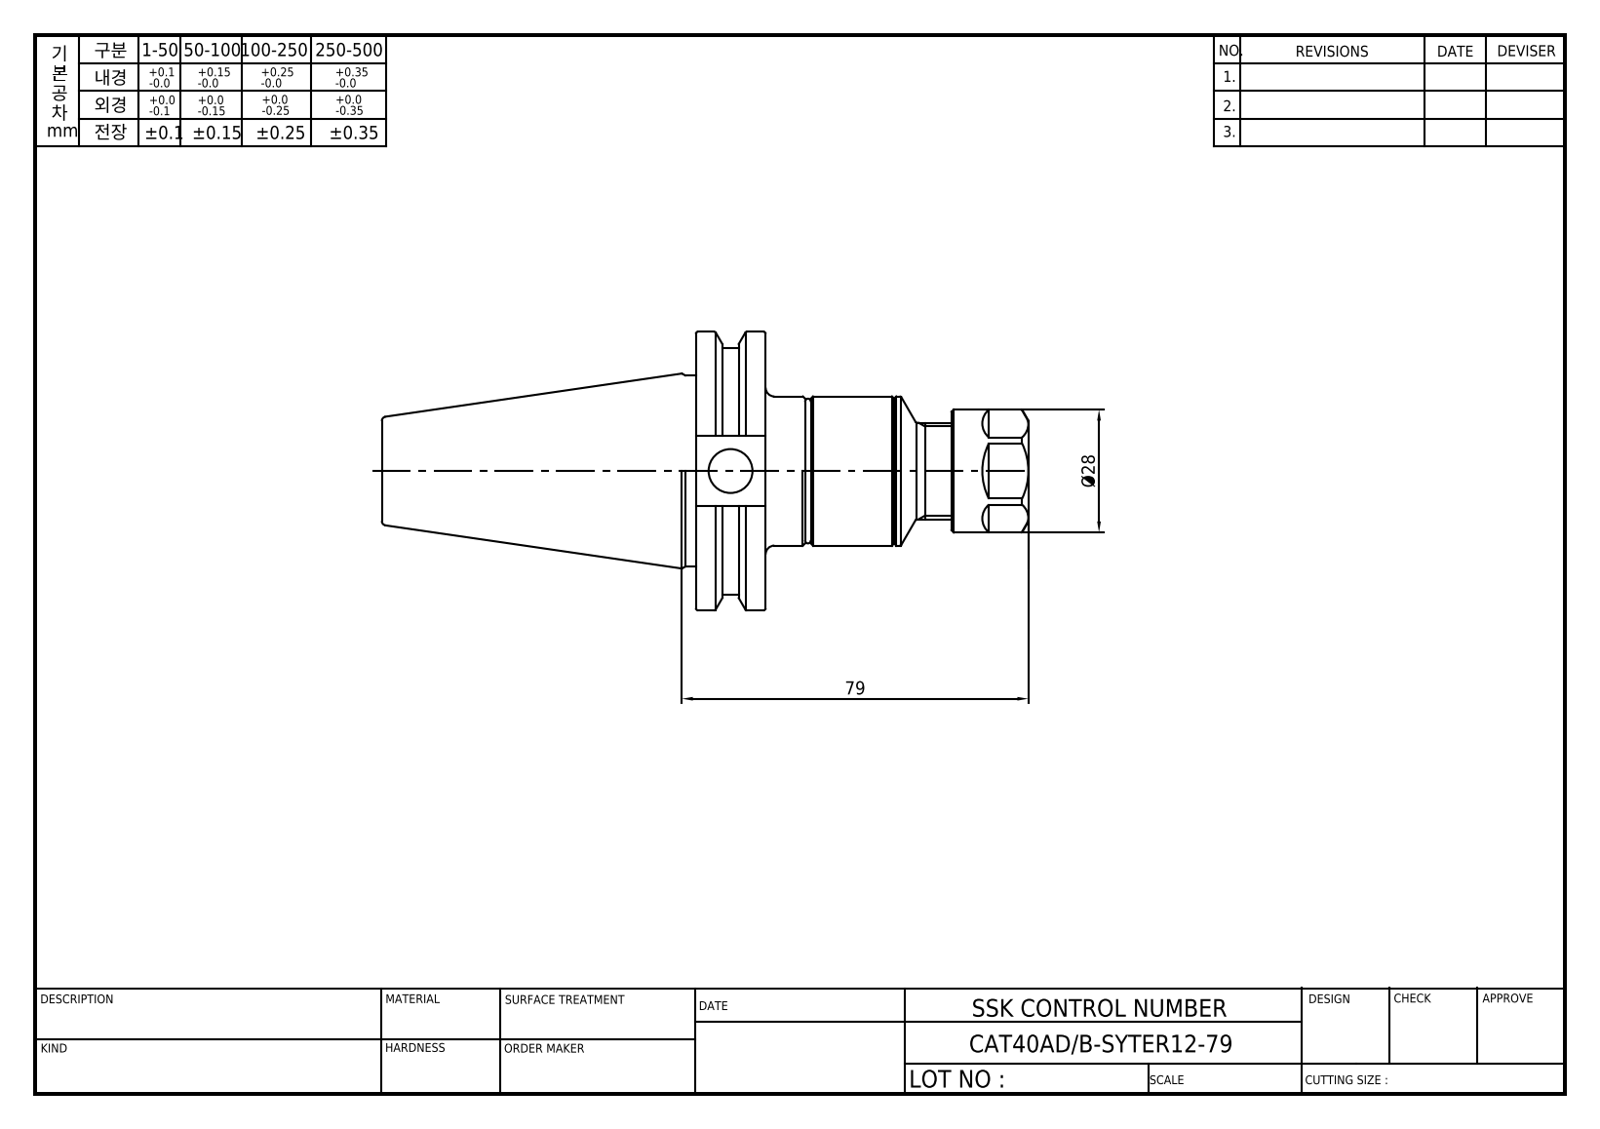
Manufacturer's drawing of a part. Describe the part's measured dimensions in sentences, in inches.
The part is named "LO-CAT40ADB-SYTER12-79; SYNCHRO-ER16-30; SYTER16-COVER(BLUE); ER16NUT". Its 3-D file was written by "Autodesk Inventor 2025 (AUTOMOTIVE_DESIGN)". It is 4 solids with 199 faces: 78 planar, 64 cylindrical and 57 other. Overall it measures 5.797 by 2.5 by 2.405 inches. Its volume is 8.329 cubic inches and its surface area 60.9 square inches. Round holes: 6 of diameter 0.157, 4 of diameter 0.128, 4 of diameter 0.161, 2 of diameter 0.165, 1 of diameter 0.039, 1 of diameter 0.205, 1 of diameter 0.375, 1 of diameter 0.394, 1 of diameter 0.402, 1 of diameter 0.417, 1 of diameter 0.433, 1 of diameter 0.504. Round bosses or shafts: 1 of diameter 2.5, 1 of diameter 1.717, 1 of diameter 1.339, 1 of diameter 1.181, 1 of diameter 1.114, 1 of diameter 1.102, 1 of diameter 0.929, 1 of diameter 0.866. Partial cylindrical surfaces (rounded edges, fillets, slot ends): 2 of radius 0.303, 1 of radius 1.108. The main face-to-face distances are 0.625, 0.531, 1.064, 0.439, 0.079, 2.985, 2.36, 1.921, 1.06, 0.435. The hole center spacings are 0.333, 0.665, 0.463, 0.47, 0.471, 0.478, 0.666, 0.282.
